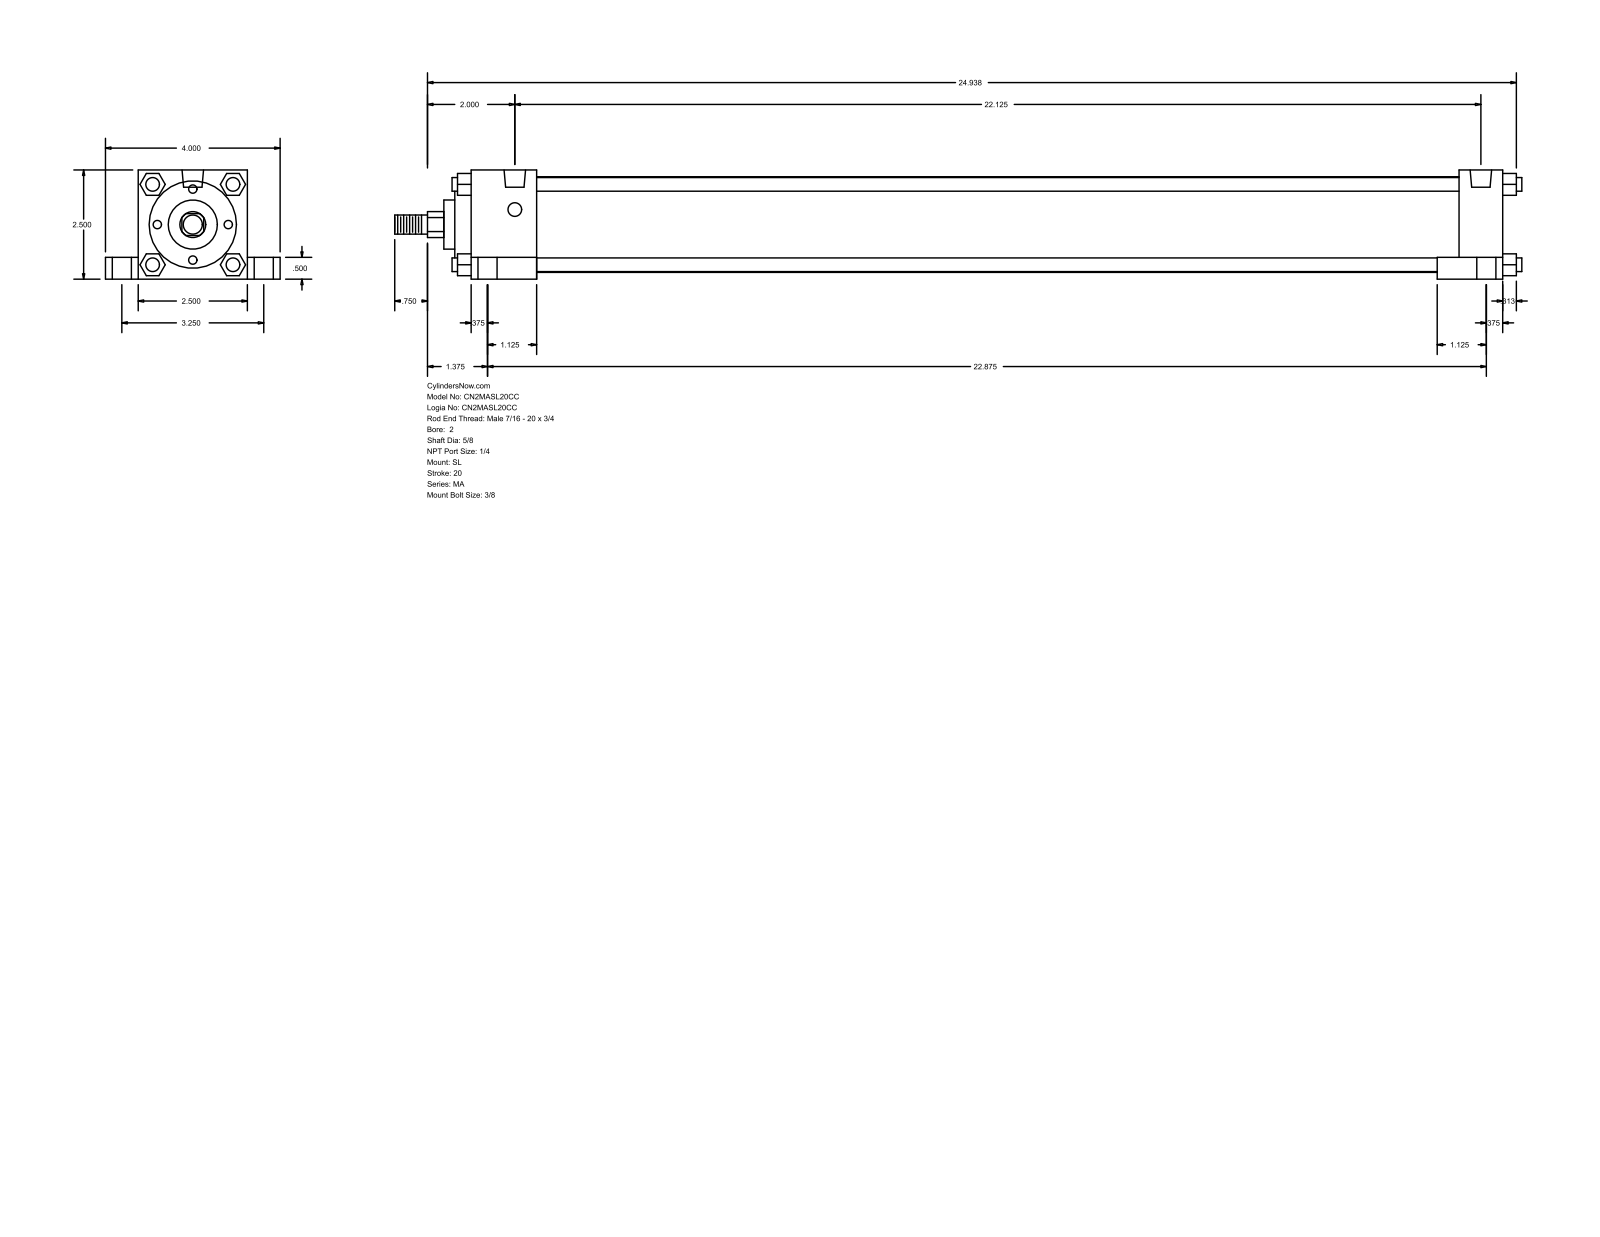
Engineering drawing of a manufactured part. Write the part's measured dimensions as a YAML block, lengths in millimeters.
part_name: "MA_SL__0200_0.625"
step_written_by: "GSSL Pune (CONFIG_CONTROL_DESIGN)"
units: millimeters
bodies: {solids: 0, faces: 150, planar: 113, cylindrical: 37, other: 0}
overall_size: [655.64, 101.6, 63.5]
round_holes:
  - {diameter: 7.94, count: 4}
  - {diameter: 11.11, count: 4}
  - {diameter: 17.46, count: 4}
  - {diameter: 12.49, count: 2}
round_bosses_or_shafts:
  - {diameter: 7.94, count: 4}
  - {diameter: 55.63, count: 1}
  - {diameter: 50.8, count: 1}
  - {diameter: 28.57, count: 1}
  - {diameter: 15.88, count: 1}
  - {diameter: 11.11, count: 1}
partial_cylinders:
  - {radius: 7.54, count: 1}
face_to_face_distances: [63.5, 12.7, 9.52, 25.4, 19.05, 82.55, 38.1, 600.08, 50.8, 561.98]
hole_center_spacings: [41.39, 44.22, 82.54, 561.97, 566.65, 579.32, 581.03, 586.86]
